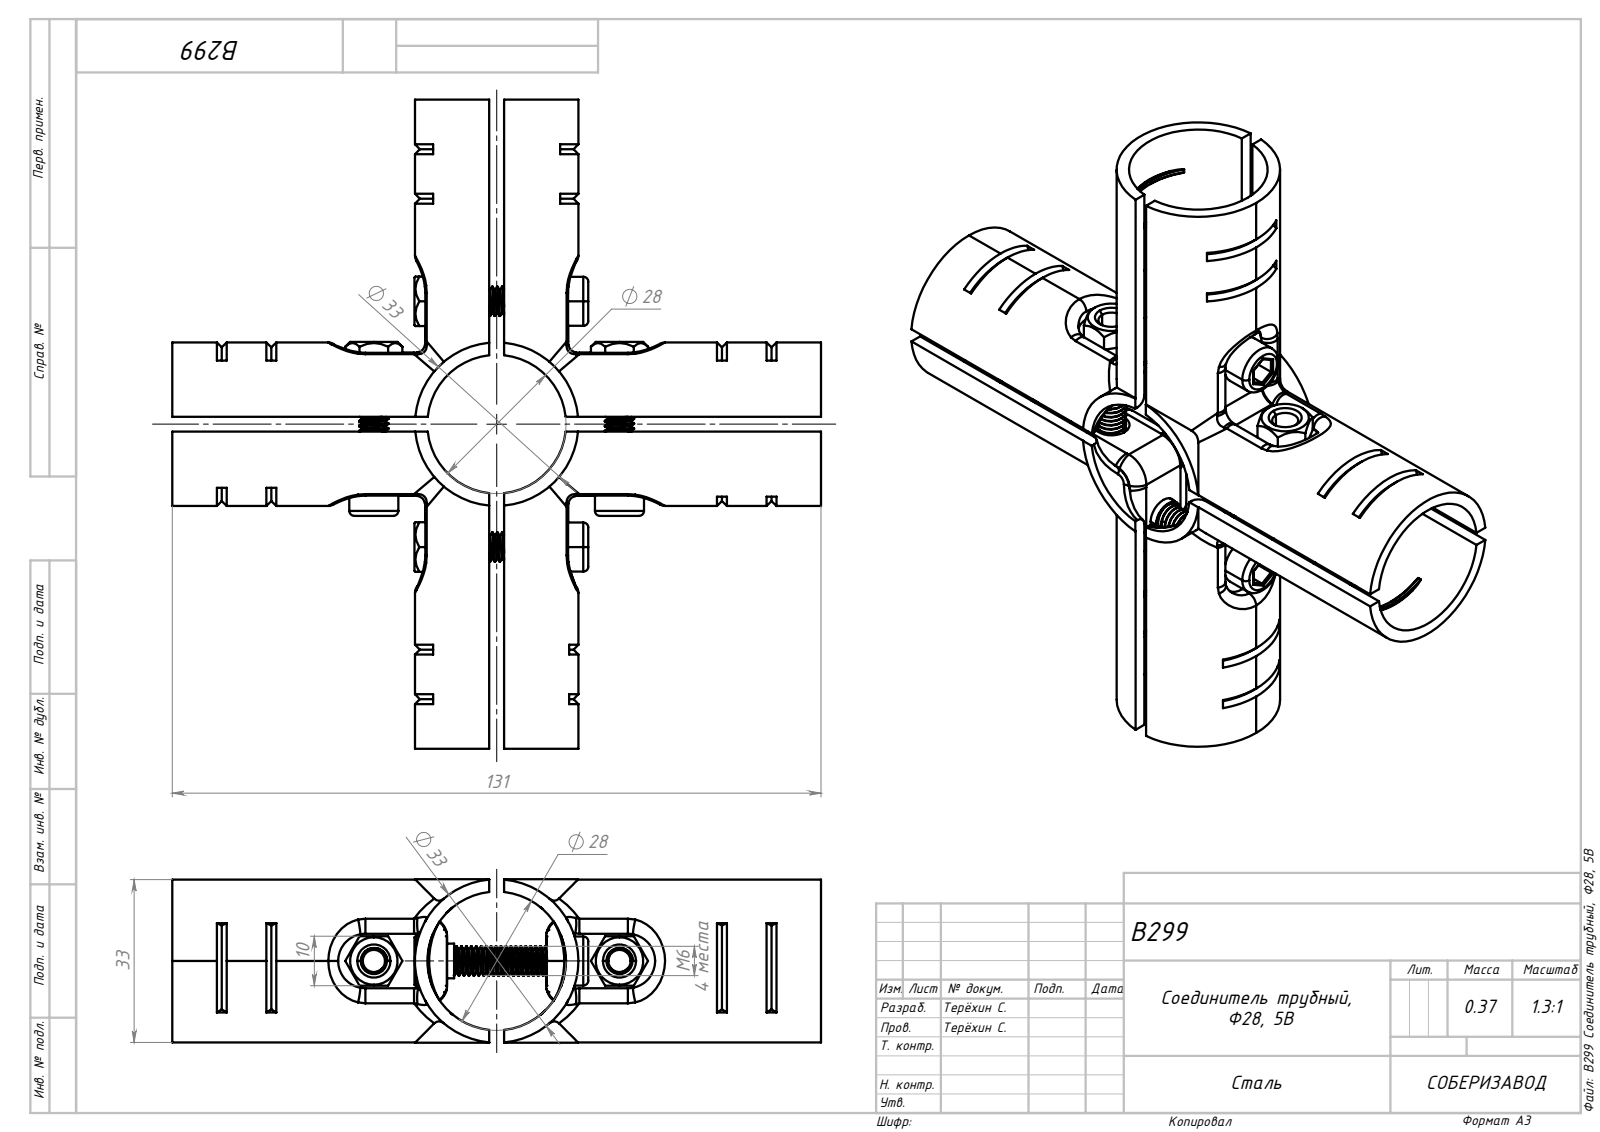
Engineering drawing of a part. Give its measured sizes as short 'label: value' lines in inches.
name: B299 Соединитель трубный, Ф28, 5B
written by: SolidWorks 2022 (AUTOMOTIVE_DESIGN)
unit: in
bodies: 12 solids, 860 faces (200 planar, 348 cylindrical, 312 other)
size: 5.157 × 5.157 × 1.299
volume: 3.247 in³; area: 75.97 in²
holes: 4× ⌀0.209, 4× ⌀0.287, 3× ⌀1.102
bosses: 4× ⌀0.39, 4× ⌀0.276, 4× ⌀0.232, 3× ⌀1.299
rounds: 22× R0.012, 8× R0.157, 4× R0.118, 4× R0.197, 4× R0.217, 4× R0.636
face distances: 0.433, 0.551, 0.118, 2.087, 2.52, 2.638, 3.071, 0.453, 0.335, 2.972
hole spacings: 0.976, 1.953
